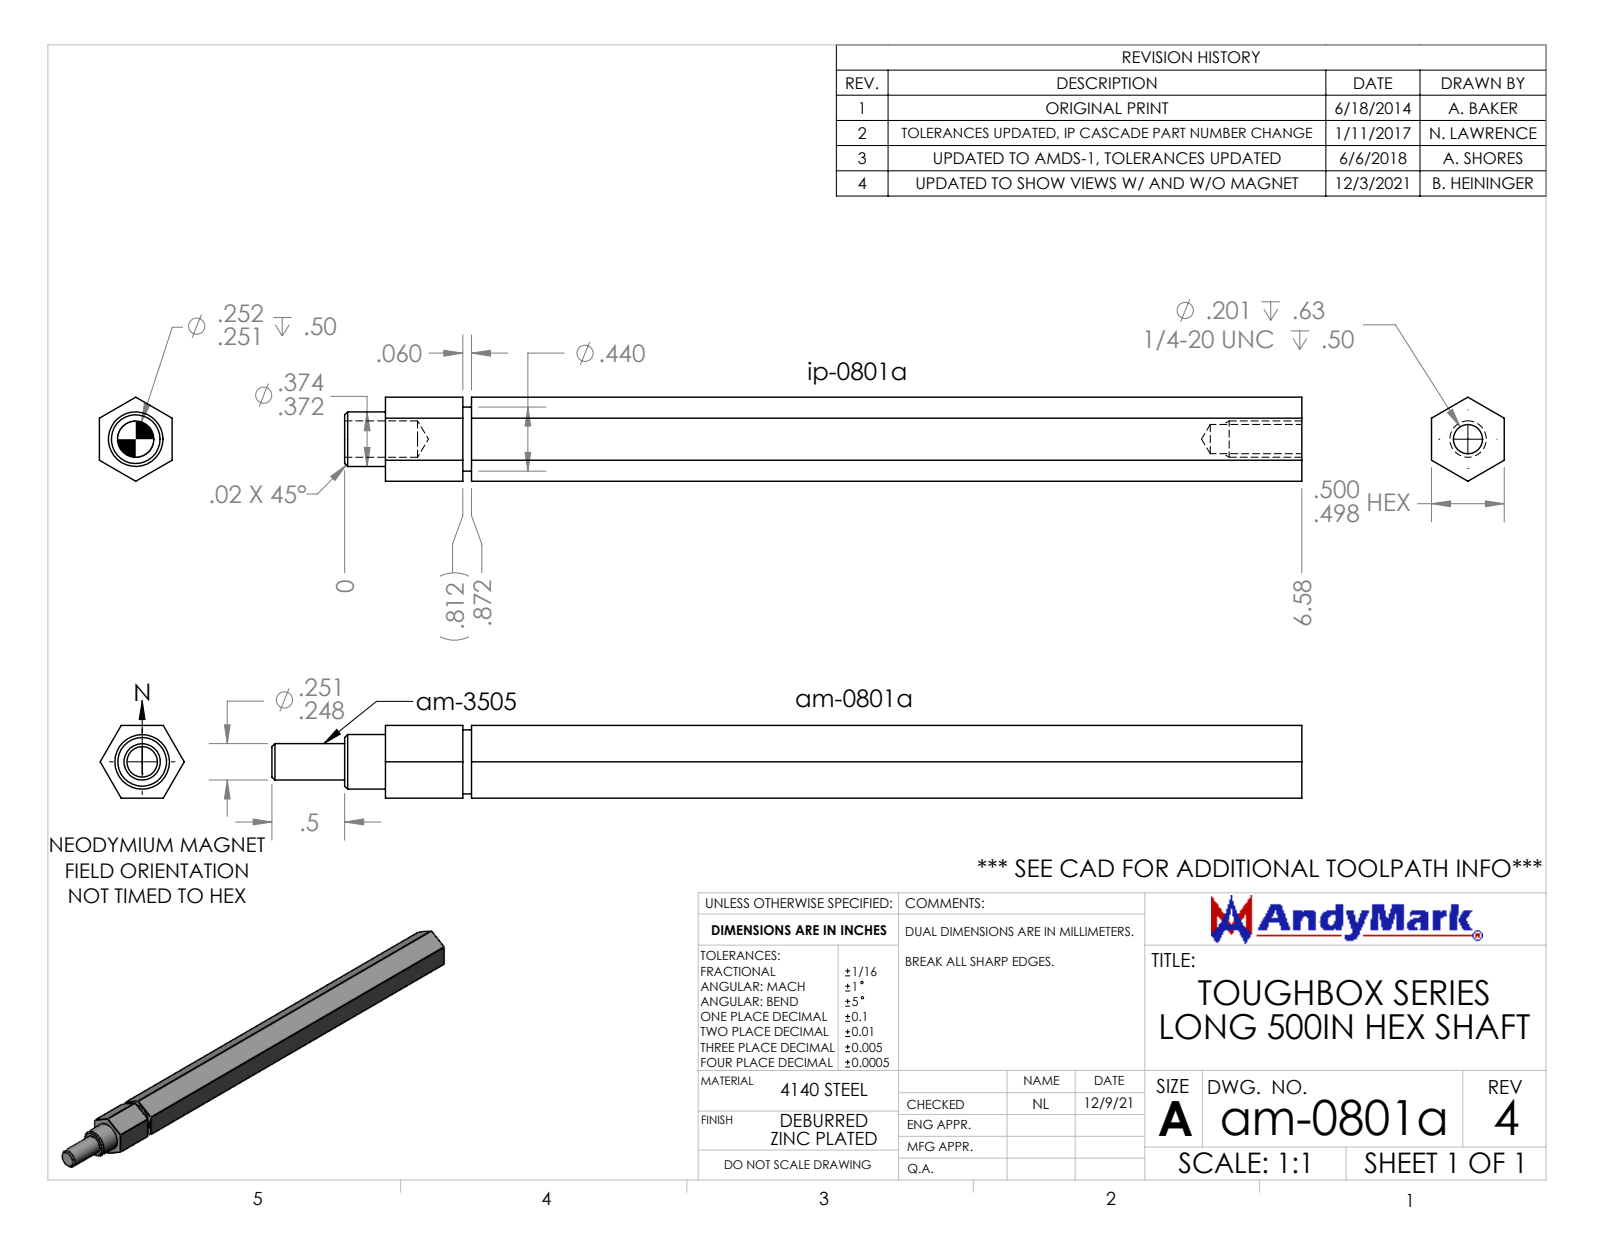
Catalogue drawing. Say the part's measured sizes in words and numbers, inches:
The part is named "am-0801a Toughbox Series Long 500Hex Output Shaft REV4". Its 3-D file was written by "SolidWorks 2021 (AUTOMOTIVE_DESIGN)". It is 2 solids with 37 faces: 19 planar, 10 cylindrical and 8 other. Overall it measures 7.08 by 0.577 by 0.5 inches. Its volume is 1.369 cubic inches and its surface area 13.05 square inches. Round holes: 1 of diameter 0.201, 1 of diameter 0.25. Round bosses or shafts: 1 of diameter 0.44, 1 of diameter 0.375. The main face-to-face distances are 0.5, 6.3, 6.58, 0.28, 5.708, 0.592, 0.872, 5.768, 0.06, 0.532.
